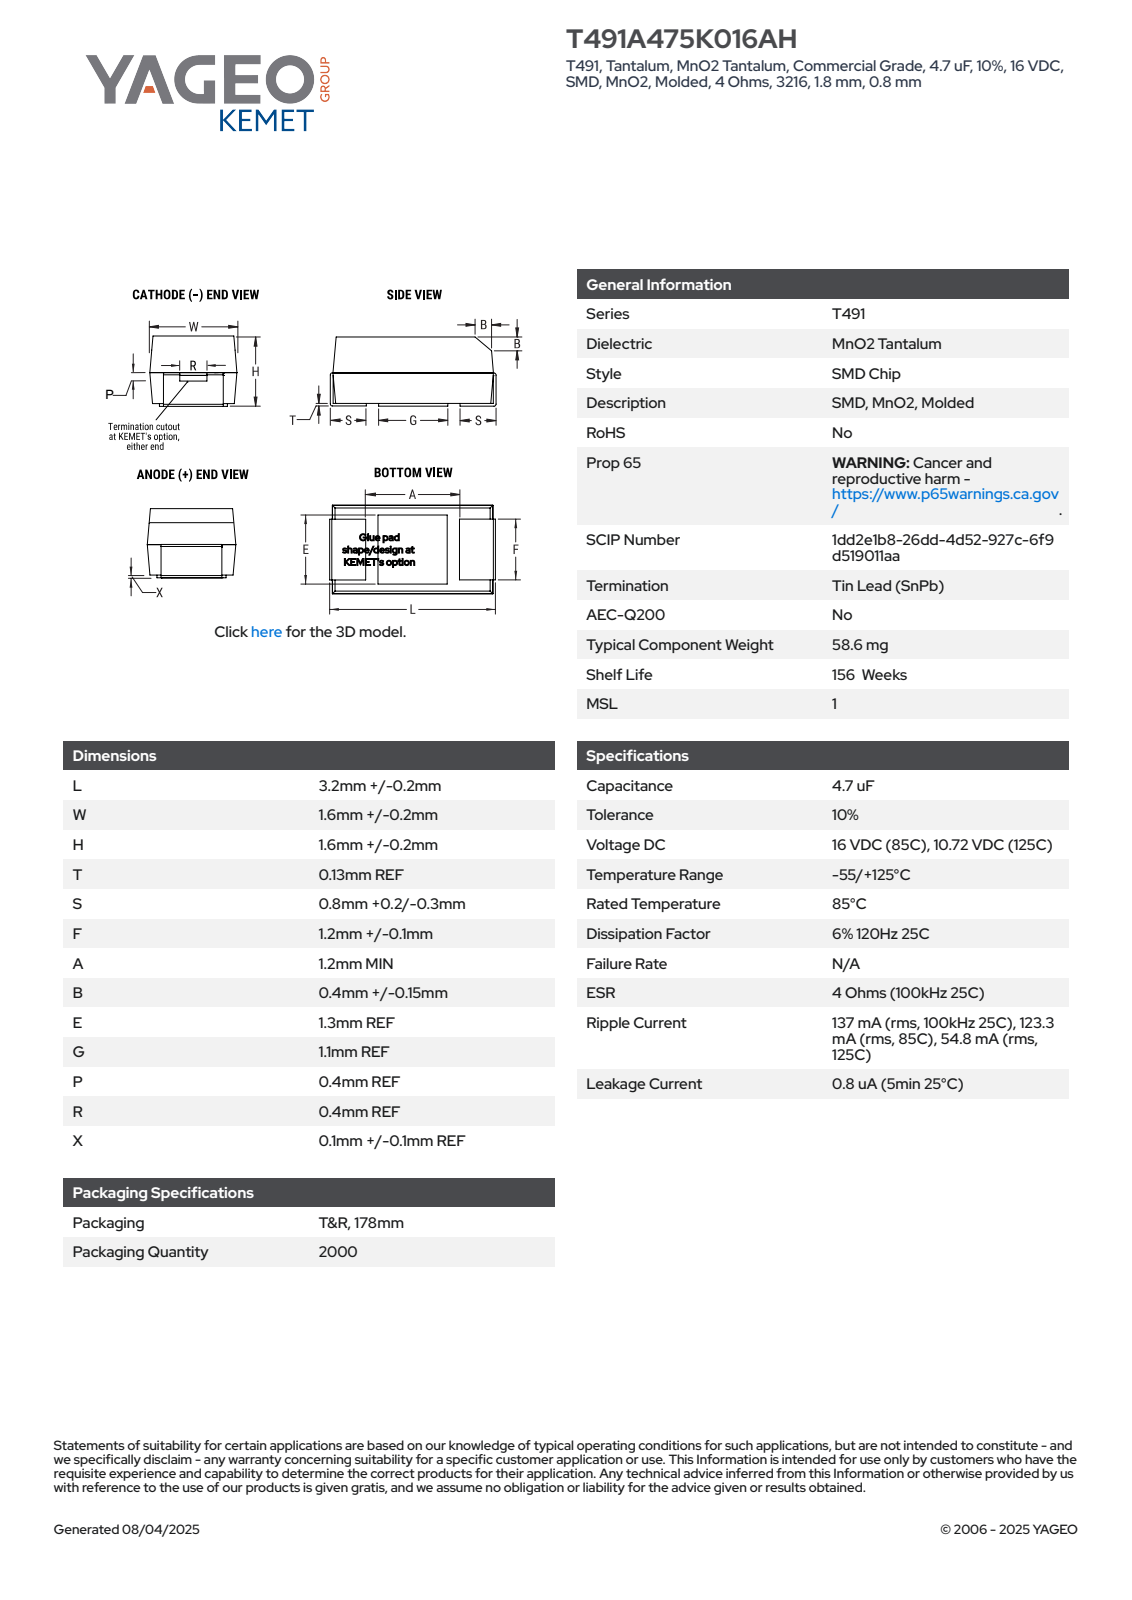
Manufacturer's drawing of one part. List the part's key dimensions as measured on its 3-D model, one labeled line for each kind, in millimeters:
Part name (STEP PRODUCT): CTSM_TCM2NK_3216_L3.4W1.8H1.8T0.13S0.8F1.3A1.2B0.55E1.3G1.1P0.4R0.4X0.2
STEP written by: SolidWorks 2020 (AUTOMOTIVE_DESIGN)
Units: millimetres
Bodies: 4 solids, 100 faces (95 planar, 5 cylindrical, 0 other)
Overall size (bounding box): 3.4 × 1.8 × 1.8
Volume: 9 mm³ · Surface area: 34 mm²
Partial cylindrical surfaces — rounded edges, fillets, slot ends (radius × count): R0.1 ×4
Main face-to-face distances: 1.79, 1.8, 1.6, 1.67, 3.27, 3.4, 3.14, 1.15, 2.25, 1.02
